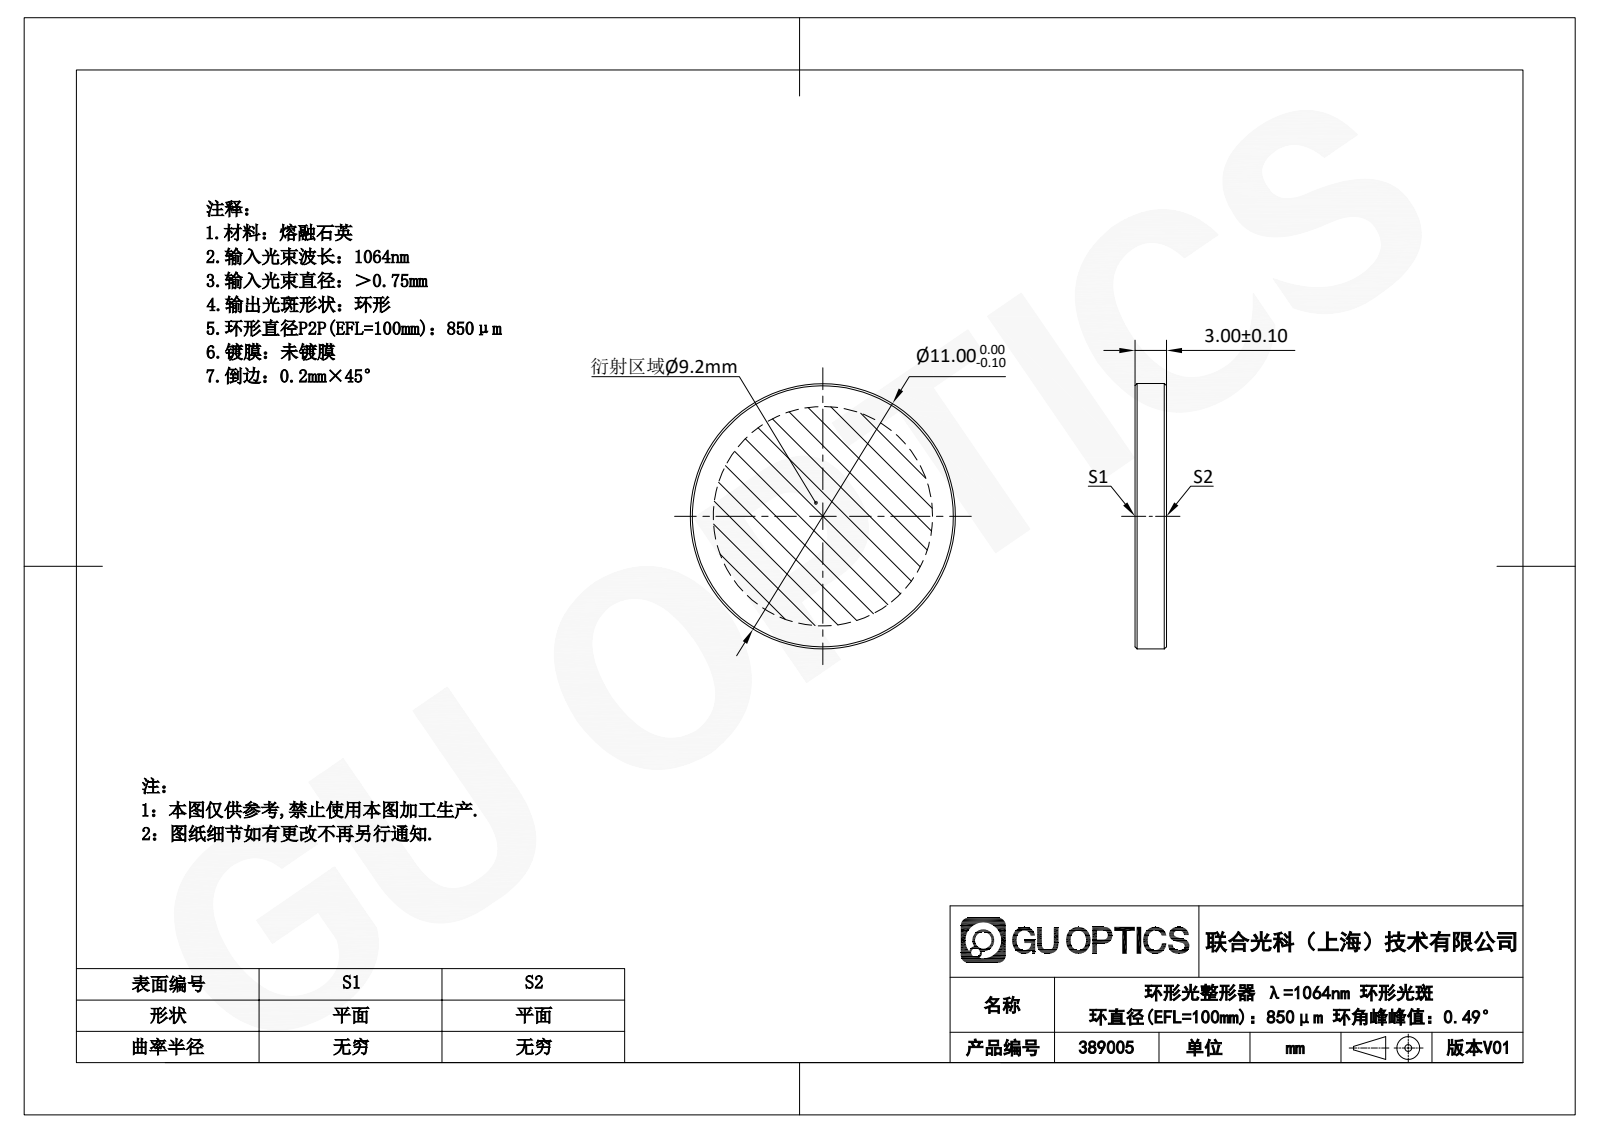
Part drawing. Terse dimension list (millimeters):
written by: SolidWorks 2020 (CONFIG_CONTROL_DESIGN)
unit: mm
bodies: 1 solid, 5 faces (2 planar, 1 cylindrical, 2 other)
size: 11 × 11 × 3
volume: 284 mm³; area: 286 mm²
bosses: 1× ⌀11
face distances: 3
